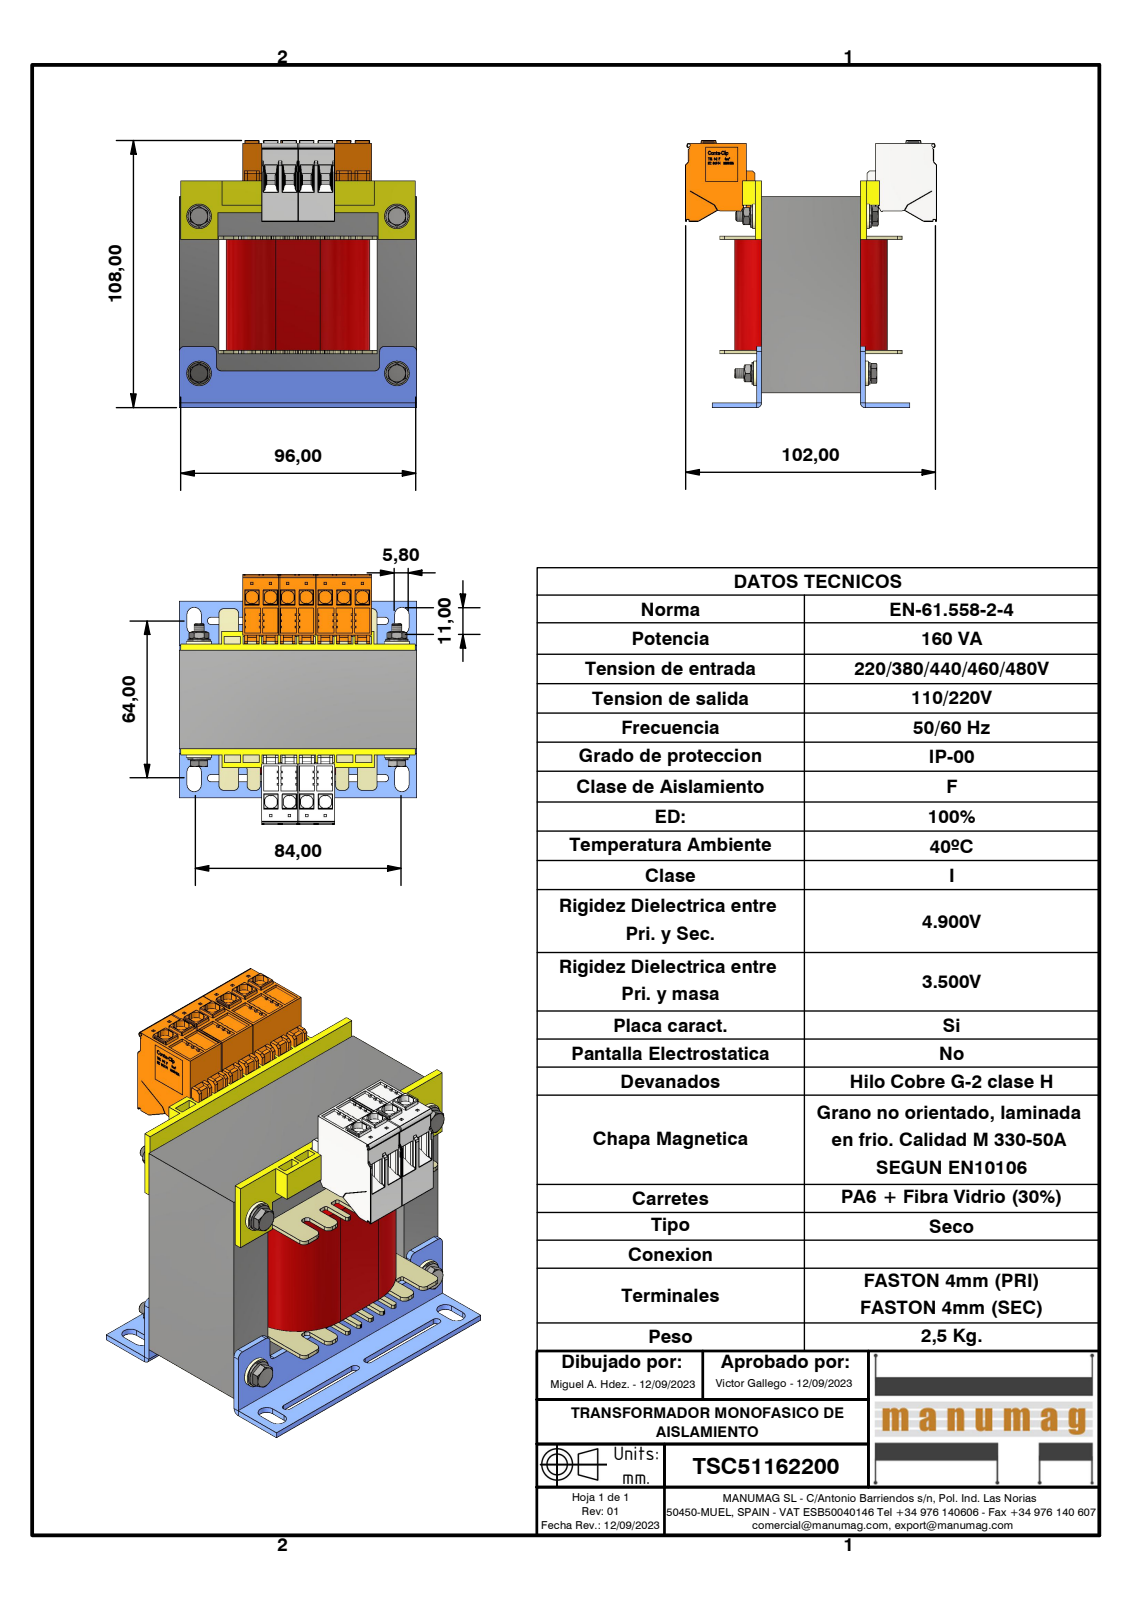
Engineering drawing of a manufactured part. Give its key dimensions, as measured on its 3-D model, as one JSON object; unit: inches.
{"part_name": "TSC51162200; EI96 x 80 - 40 (RC32); EI 96 X 80 - 40; AF32DIN (+8 more)", "step_written_by": "Autodesk Inventor 2023 (AUTOMOTIVE_DESIGN)", "units": "inches", "bodies": {"solids": 35, "faces": 9280, "planar": 7534, "cylindrical": 1187, "other": 559}, "overall_size": [4.291, 4.012, 3.78], "volume_in3": 25.13, "surface_area_in2": 205, "round_holes": [[0.128, 4], [0.157, 4], [0.169, 4], [0.217, 4], [0.228, 2]], "round_bosses_or_shafts": [[0.394, 4], [0.354, 4], [0.232, 4], [0.193, 4], [0.143, 4]], "partial_cylinders_radius": [[0.006, 431], [0.008, 122], [0.031, 52], [0.02, 30], [0.079, 22], [0.012, 12], [0.106, 11], [0.197, 10]], "face_to_face_distances": [2.52, 0.63, 1.575, 1.26, 1.89, 3.15, 0.079, 0.02, 1.878, 1.772], "hole_center_spacings": [2.52, 3.15, 4.033]}
